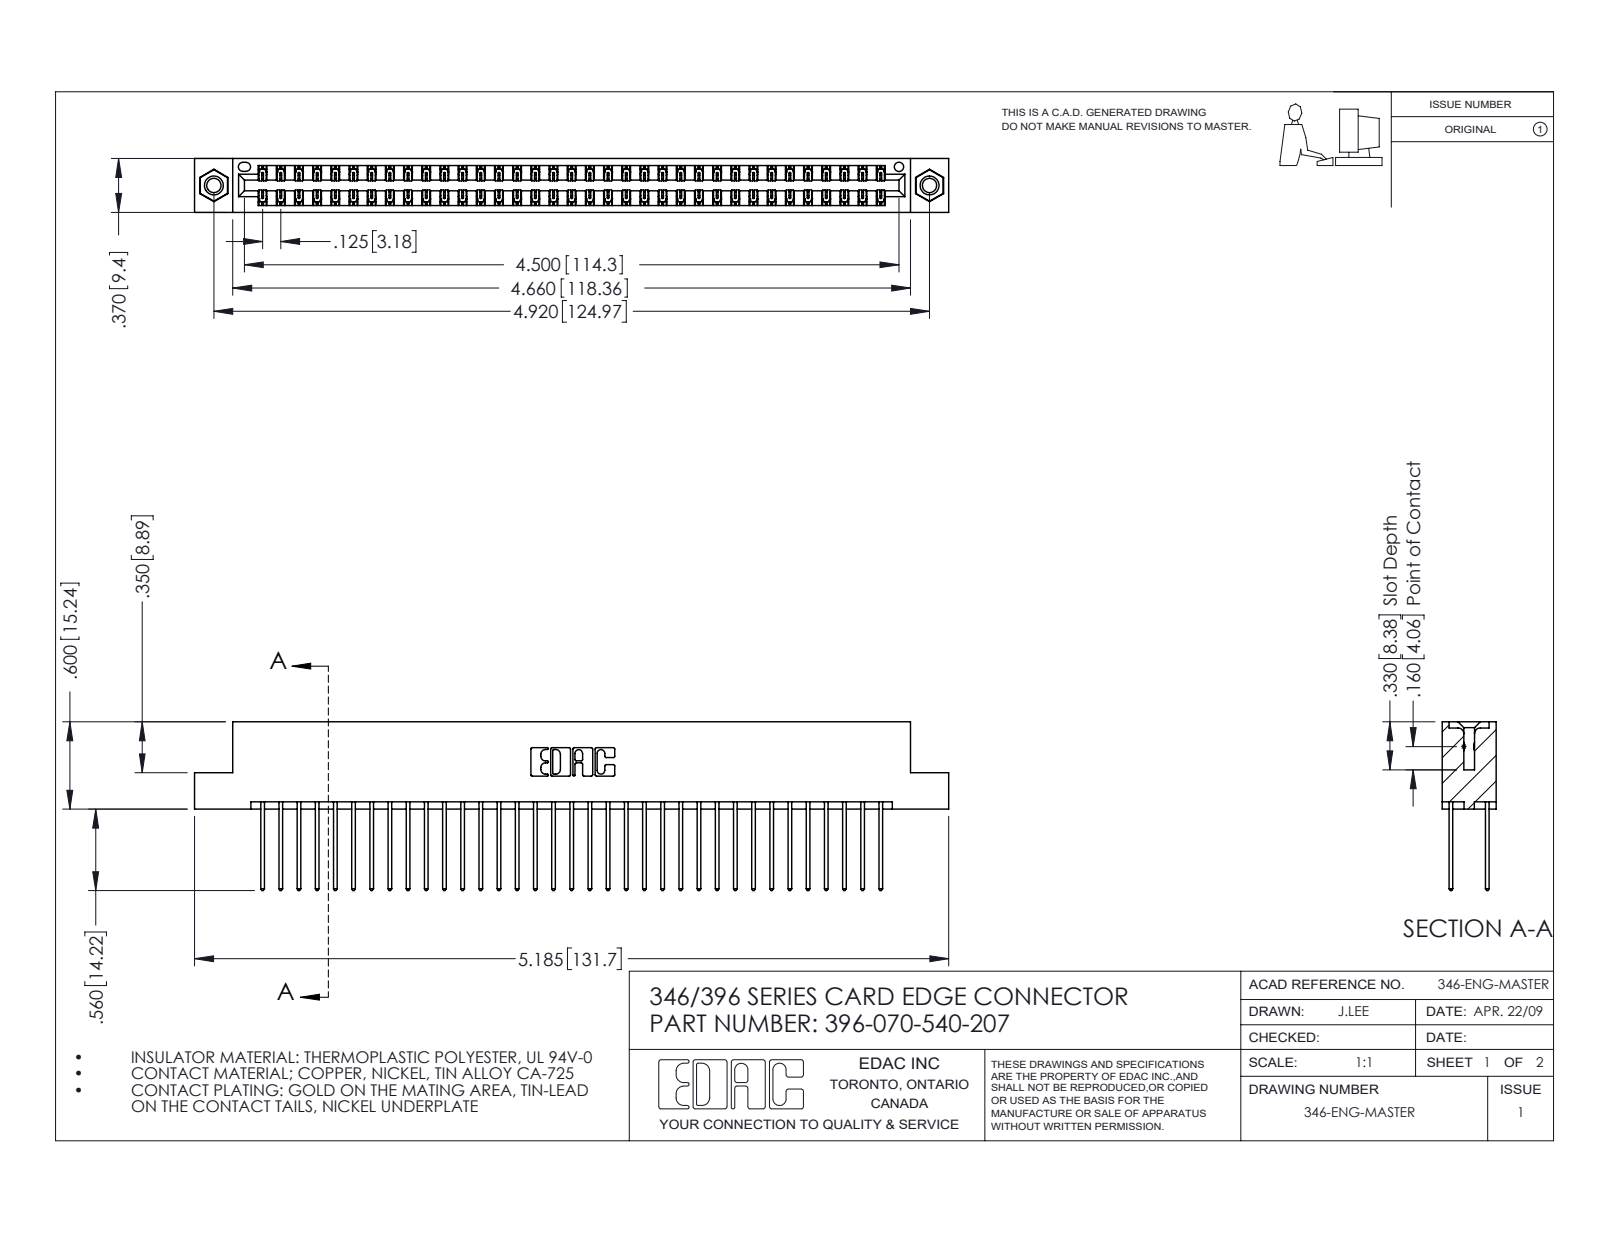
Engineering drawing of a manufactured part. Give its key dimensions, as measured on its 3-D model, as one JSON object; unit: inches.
{"part_name": "396-070-540-207; 345-292-001_345-293-140; 346 Part_Flush Mounting Lugs - 0.156 Dia-TI; 345-250-001_345-250-005-103", "step_written_by": "SolidWorks 2016 (CONFIG_CONTROL_DESIGN)", "units": "inches", "bodies": {"solids": 73, "faces": 3822, "planar": 2558, "cylindrical": 1248, "other": 16}, "overall_size": [5.185, 1.16, 0.37], "volume_in3": 0.796, "surface_area_in2": 29.61, "round_holes": [[0.098, 2], [0.125, 2], [0.156, 2], [0.064, 1]], "round_bosses_or_shafts": [[0.155, 2]], "partial_cylinders_radius": [[0.006, 105], [0.01, 70], [0.01, 22], [0.007, 6], [0.031, 6], [0.026, 3], [0.014, 2], [0.022, 2]], "face_to_face_distances": [0.048, 0.322, 0.25, 0.072, 0.298, 0.025, 0.37, 0.275, 0.148, 0.222], "hole_center_spacings": [0.246, 4.711, 4.92]}
